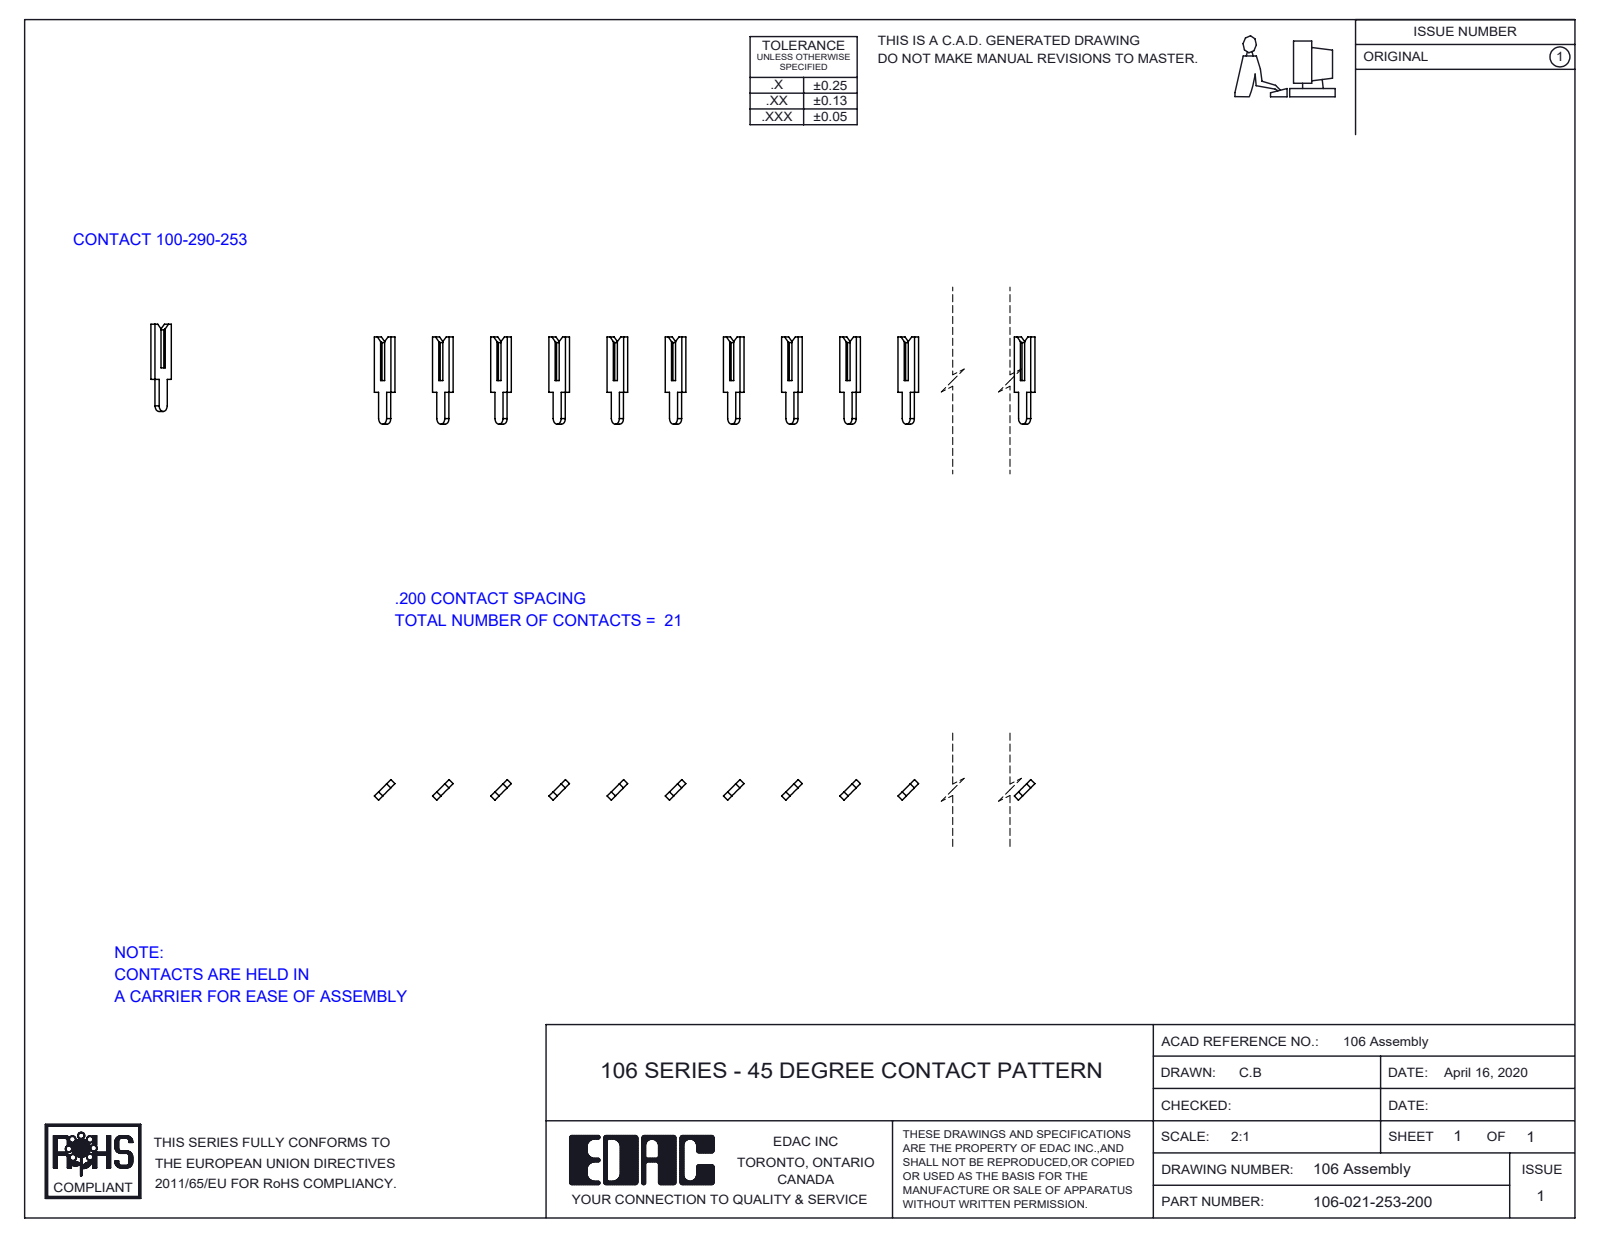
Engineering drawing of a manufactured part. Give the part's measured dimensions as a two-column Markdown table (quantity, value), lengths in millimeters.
| quantity | value |
| --- | --- |
| part name | 100-290-001_100-290-253; 106-021-253-200 |
| STEP written by | SolidWorks 2016 (CONFIG_CONTROL_DESIGN) |
| units | millimeters |
| bodies | 21 solids, 420 faces (399 planar, 21 cylindrical, 0 other) |
| overall size | 103.4 × 7.6 × 1.8 |
| volume | 100 mm³ |
| surface area | 723 mm² |
| partial cylindrical surfaces (radius × count) | 0.5 × 21 |
| main face-to-face distances | 3.6, 21.5, 7.2, 25.1, 18, 14.4, 10.8, 28.7, 10.8, 46.7 |
